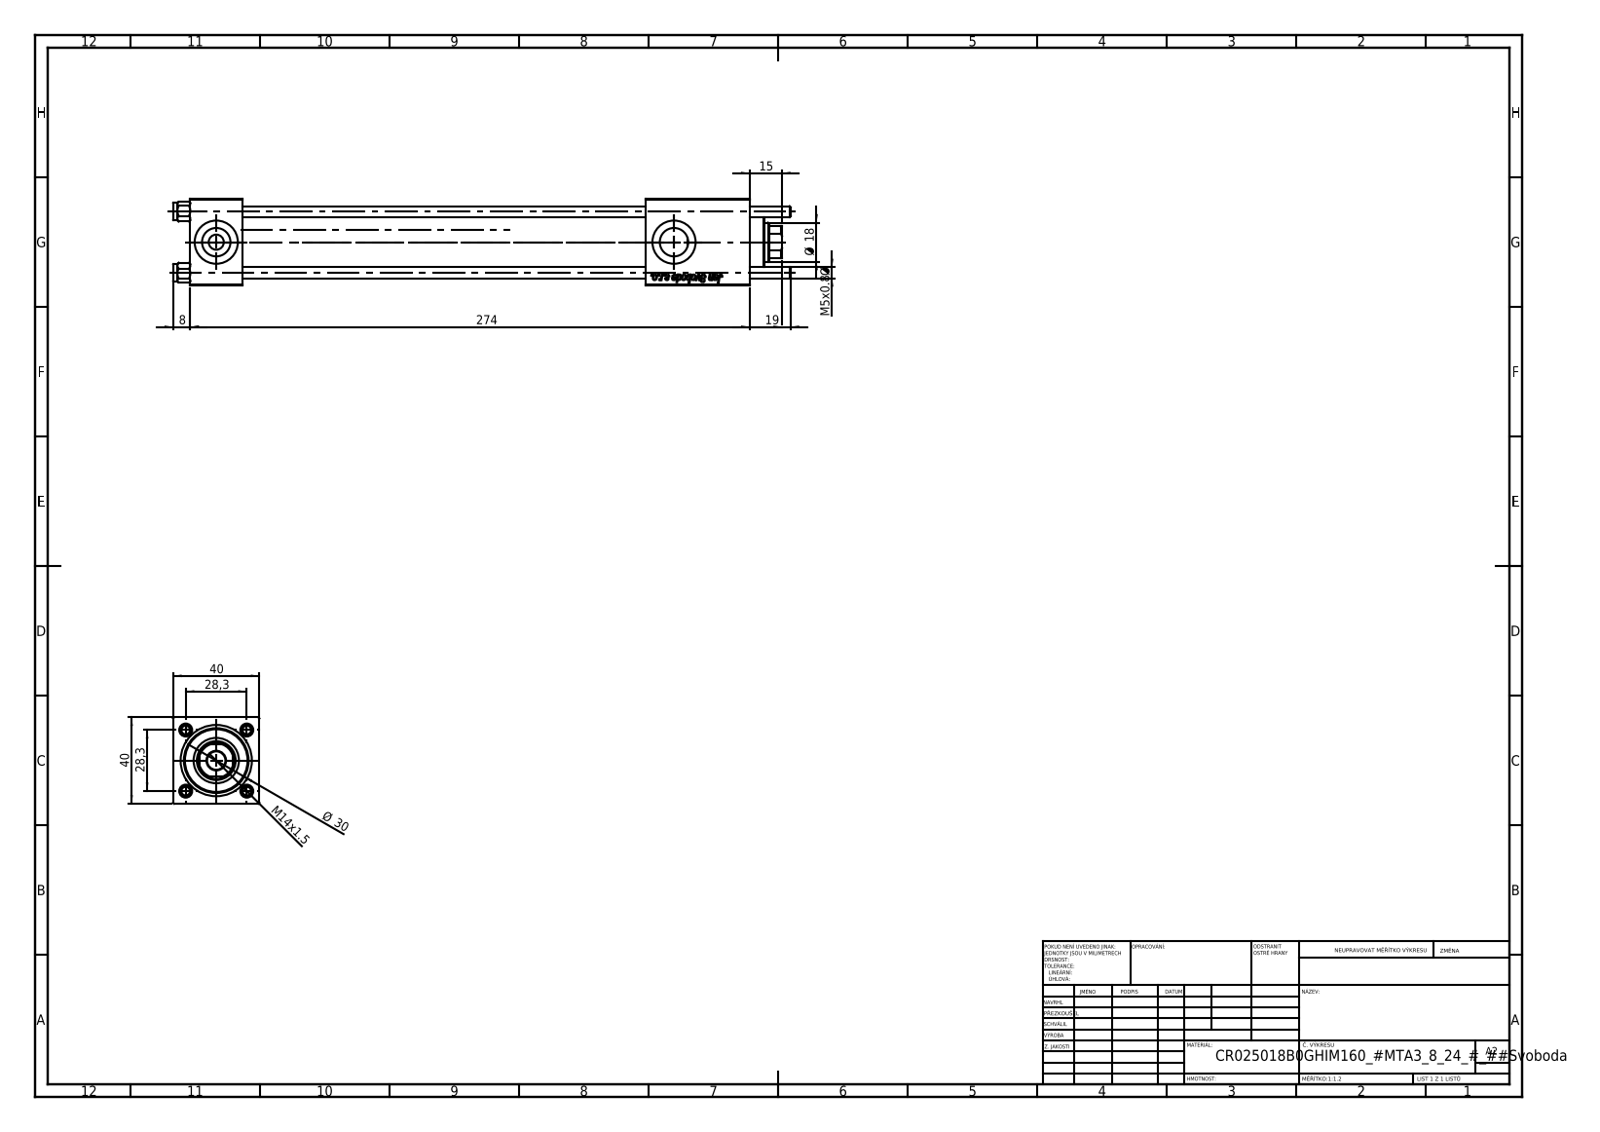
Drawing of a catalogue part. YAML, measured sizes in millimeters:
part_name: "V215CR_B-1; V215_VC_A; NUT_M5_B; V215CR_VCP_B (+1 more)"
step_written_by: "SolidWorks 2019 (CONFIG_CONTROL_DESIGN)"
units: millimeters
bodies: {solids: 11, faces: 1152, planar: 428, cylindrical: 76, other: 648}
overall_size: [286, 40, 40]
volume: 236057
surface_area: 102238
round_holes:
  - {diameter: 5, count: 4}
  - {diameter: 20, count: 3}
  - {diameter: 7, count: 2}
  - {diameter: 13.16, count: 2}
  - {diameter: 8.5, count: 1}
  - {diameter: 18, count: 1}
  - {diameter: 21, count: 1}
  - {diameter: 25, count: 1}
  - {diameter: 30, count: 1}
round_bosses_or_shafts:
  - {diameter: 8, count: 4}
  - {diameter: 31, count: 1}
partial_cylinders:
  - {radius: 8.5, count: 1}
face_to_face_distances: [40, 24, 211, 187, 230.3, 206.3, 19.3, 259, 235, 48]
hole_center_spacings: [20.01, 28.3, 40.02, 212]
